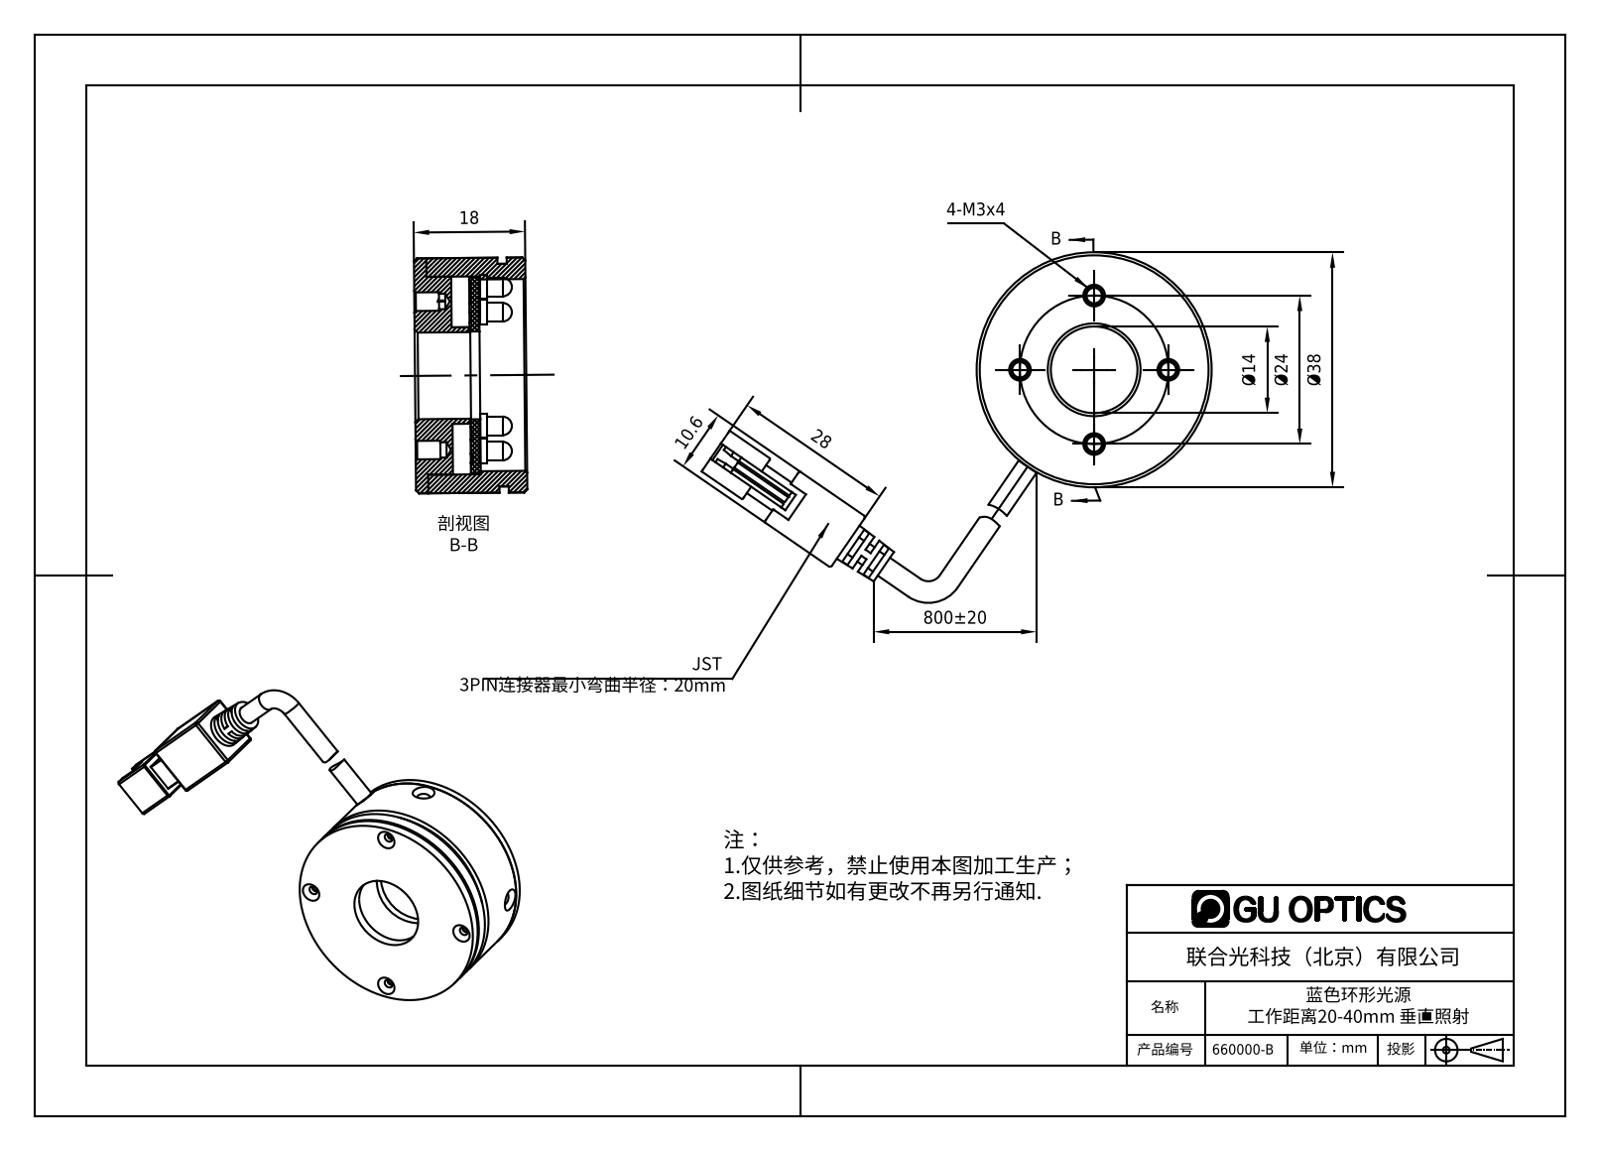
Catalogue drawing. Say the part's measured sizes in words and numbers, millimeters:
The part is named "660000-B". Its 3-D file was written by "SolidWorks 2016 (AUTOMOTIVE_DESIGN)". It is 6 solids with 503 faces: 184 planar, 232 cylindrical and 87 other. Overall it measures 84.41 by 51.27 by 22 millimeters. Its volume is 14 550 cubic millimeters and its surface area 13 826 square millimeters. Round holes: 35 of diameter 3.8, 4 of diameter 1.25, 4 of diameter 1.7, 4 of diameter 2.5, 4 of diameter 3, 2 of diameter 1.6, 2 of diameter 2, 2 of diameter 2.4, 1 of diameter 14, 1 of diameter 14.2, 1 of diameter 31. Round bosses or shafts: 2 of diameter 3.5, 1 of diameter 38, 1 of diameter 36, 1 of diameter 32, 1 of diameter 31.8, 1 of diameter 15.6. Partial cylindrical surfaces (rounded edges, fillets, slot ends): 15 of radius 0.1, 13 of radius 0.2, 12 of radius 0.4, 1 of radius 0.3, 1 of radius 0.68, 1 of radius 1.4, 1 of radius 1.6, 1 of radius 6.5. The main face-to-face distances are 2, 18, 20, 4.5, 7.5, 16, 10.5, 8.5, 9.5, 6. The hole center spacings are 9.5, 13.5, 18.52, 4.23, 14.85, 15.21, 17.12, 10.61.
